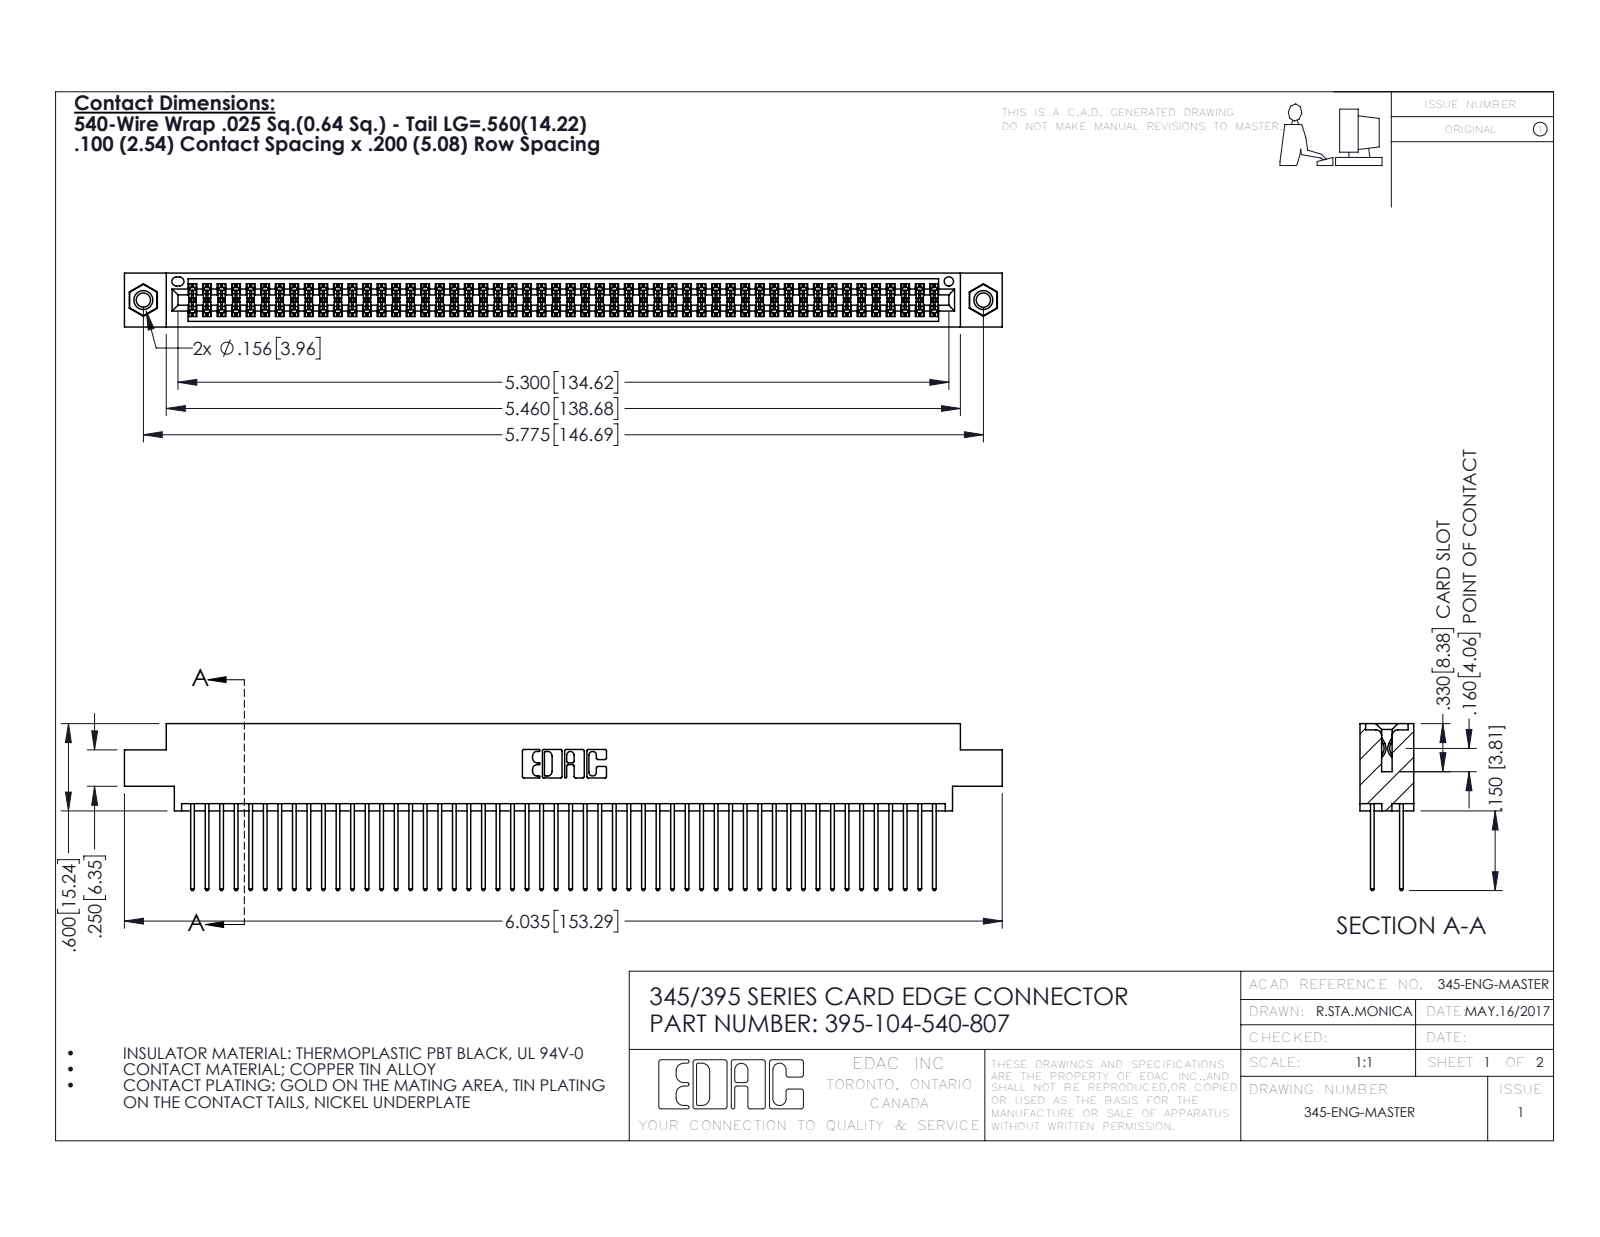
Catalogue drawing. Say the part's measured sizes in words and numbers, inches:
The part is named "395-104-540-807; 345-250-001_345-250-005-103; 345 Part_0.170 Offset - 0.156 Dia-TI; 345-292-001_345-293-140". Its 3-D file was written by "SolidWorks 2016 (CONFIG_CONTROL_DESIGN)". It is 107 solids with 5390 faces: 3548 planar, 1826 cylindrical and 16 other. Overall it measures 6.035 by 1.147 by 0.37 inches. Its volume is 0.931 cubic inches and its surface area 38.34 square inches. Round holes: 2 of diameter 0.098, 2 of diameter 0.125, 2 of diameter 0.156, 1 of diameter 0.064. Round bosses or shafts: 2 of diameter 0.155. Partial cylindrical surfaces (rounded edges, fillets, slot ends): 156 of radius 0.006, 104 of radius 0.01, 22 of radius 0.01, 6 of radius 0.007, 6 of radius 0.031, 3 of radius 0.026, 2 of radius 0.014, 2 of radius 0.019. The main face-to-face distances are 0.072, 0.298, 0.2, 0.098, 0.272, 0.025, 0.37, 0.225, 0.175, 0.149. The hole center spacings are 0.27, 5.539, 5.775.
